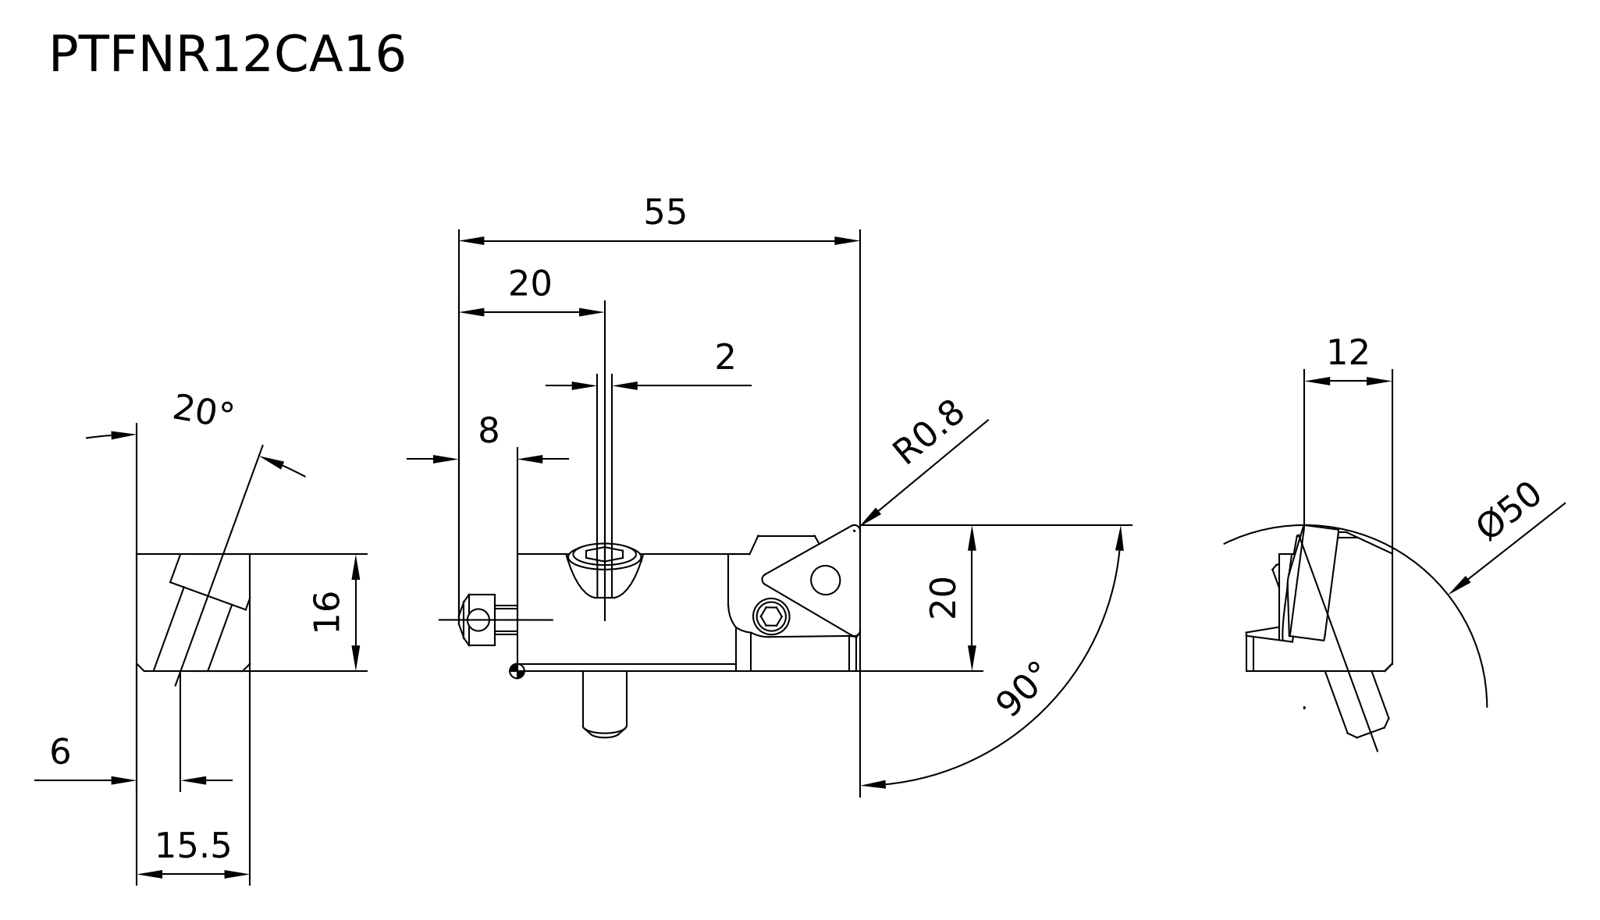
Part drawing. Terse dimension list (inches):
name: PTFNR12CA16__ASM
written by: SIEMENS PLM Software NX 10.0 (AUTOMOTIVE_DESIGN)
unit: in
bodies: 7 solids, 228 faces (113 planar, 73 cylindrical, 42 other)
size: 2.144 × 1.109 × 0.787
volume: 0.664 in³; area: 9.241 in²
holes: 2× ⌀0.071, 2× ⌀0.165, 1× ⌀0.081, 1× ⌀0.13
bosses: 2× ⌀0.197, 2× ⌀0.118, 1× ⌀0.394, 1× ⌀0.276, 1× ⌀0.236, 1× ⌀0.157, 1× ⌀0.067
rounds: 12× R0.008, 7× R0.02, 4× R0.004, 3× R0.197, 2× R0.063, 2× R0.138, 2× R0.217, 1× R0.075
face distances: 0.61, 0.63, 1.829, 0.168, 0.787, 0.118, 0.086, 0.716, 0.177, 0.15
hole spacings: 1.819
